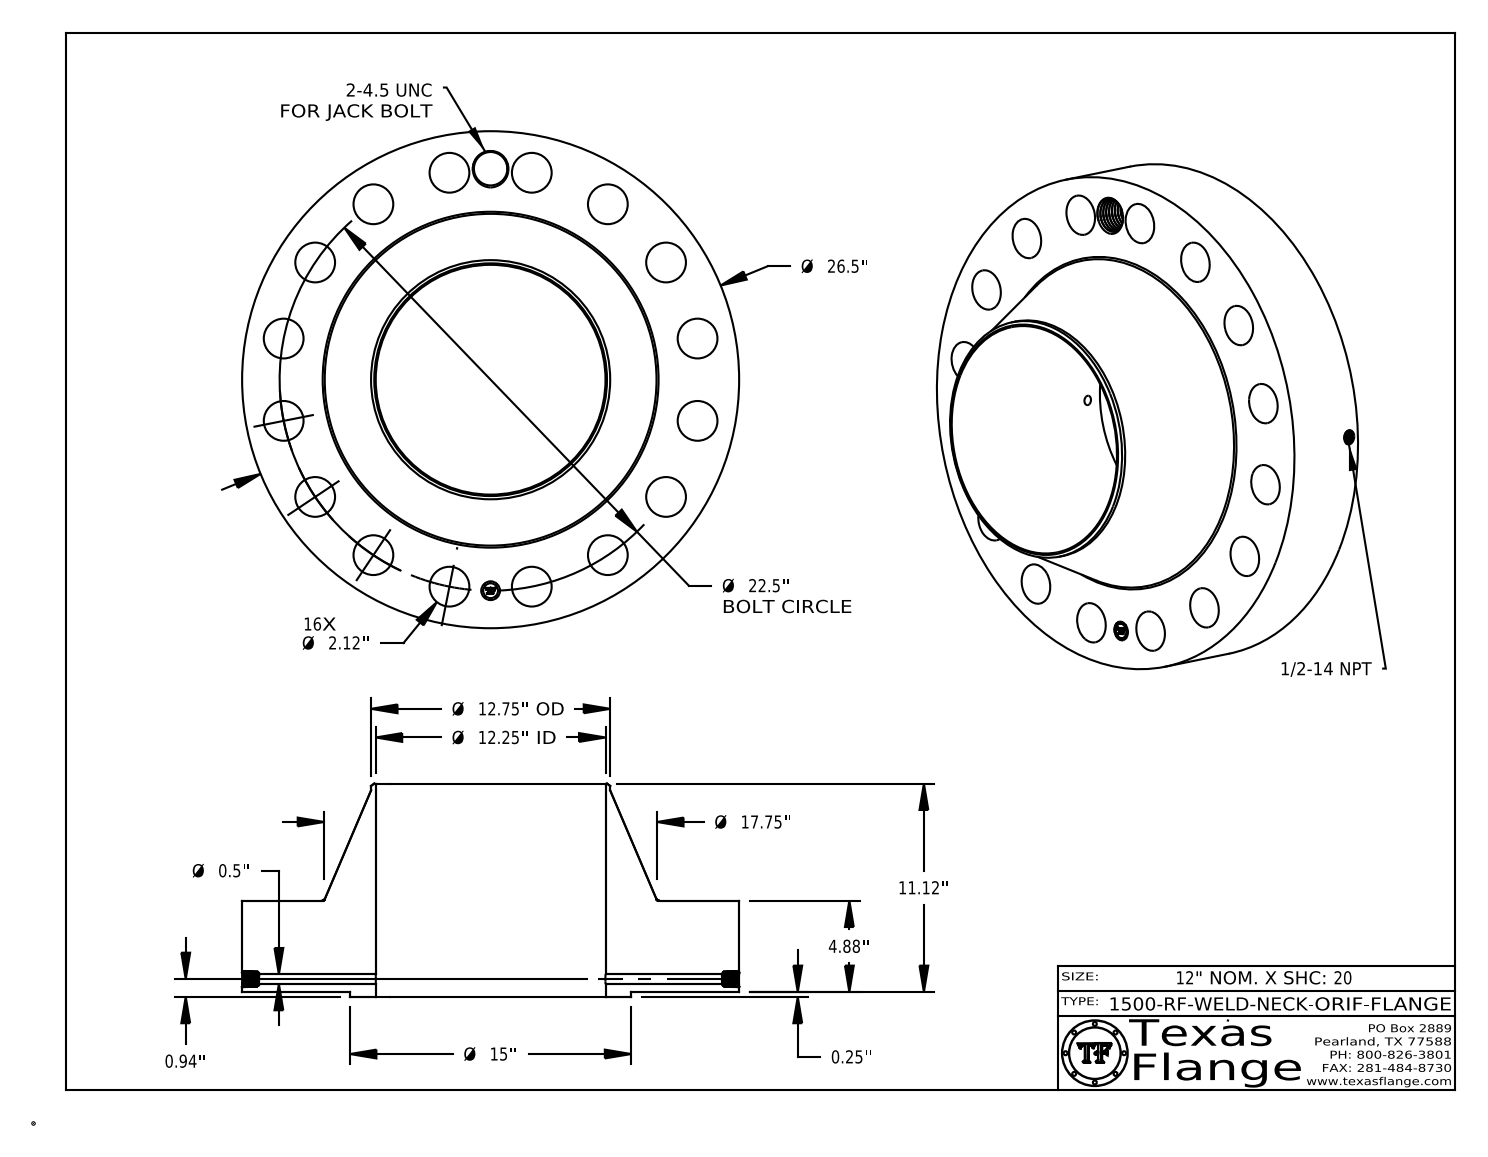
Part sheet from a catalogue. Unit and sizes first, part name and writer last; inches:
Units: inches
Overall size (bounding box): 26.5 × 26.5 × 11.37
Round holes (diameter × count): ⌀2.12 ×16, ⌀0.5 ×1, ⌀0.672 ×1, ⌀1 ×1, ⌀1.781 ×1, ⌀12.25 ×1
Round bosses / shafts (diameter × count): ⌀0.061 ×8, ⌀26.5 ×1, ⌀15 ×1, ⌀12.75 ×1, ⌀0.788 ×1
Main face-to-face distances: 4.88, 0.25, 5.13, 11.37, 11.12, 6.24, 5.115, 4.865, 0.015, 6.255
Hole centre spacings: 11.25, 8.61, 15.91, 20.787, 12.5, 18.708, 22.068, 4.389
Volume: 2 232 in³ · Surface area: 2 387 in²
Bodies: 1 solid, 827 faces (369 planar, 124 cylindrical, 334 other)
Part name (STEP PRODUCT): 1500-RF-WELD-NECK
STEP written by: CATIA V5 STEP AP214 (AUTOMOTIVE_DESIGN)
